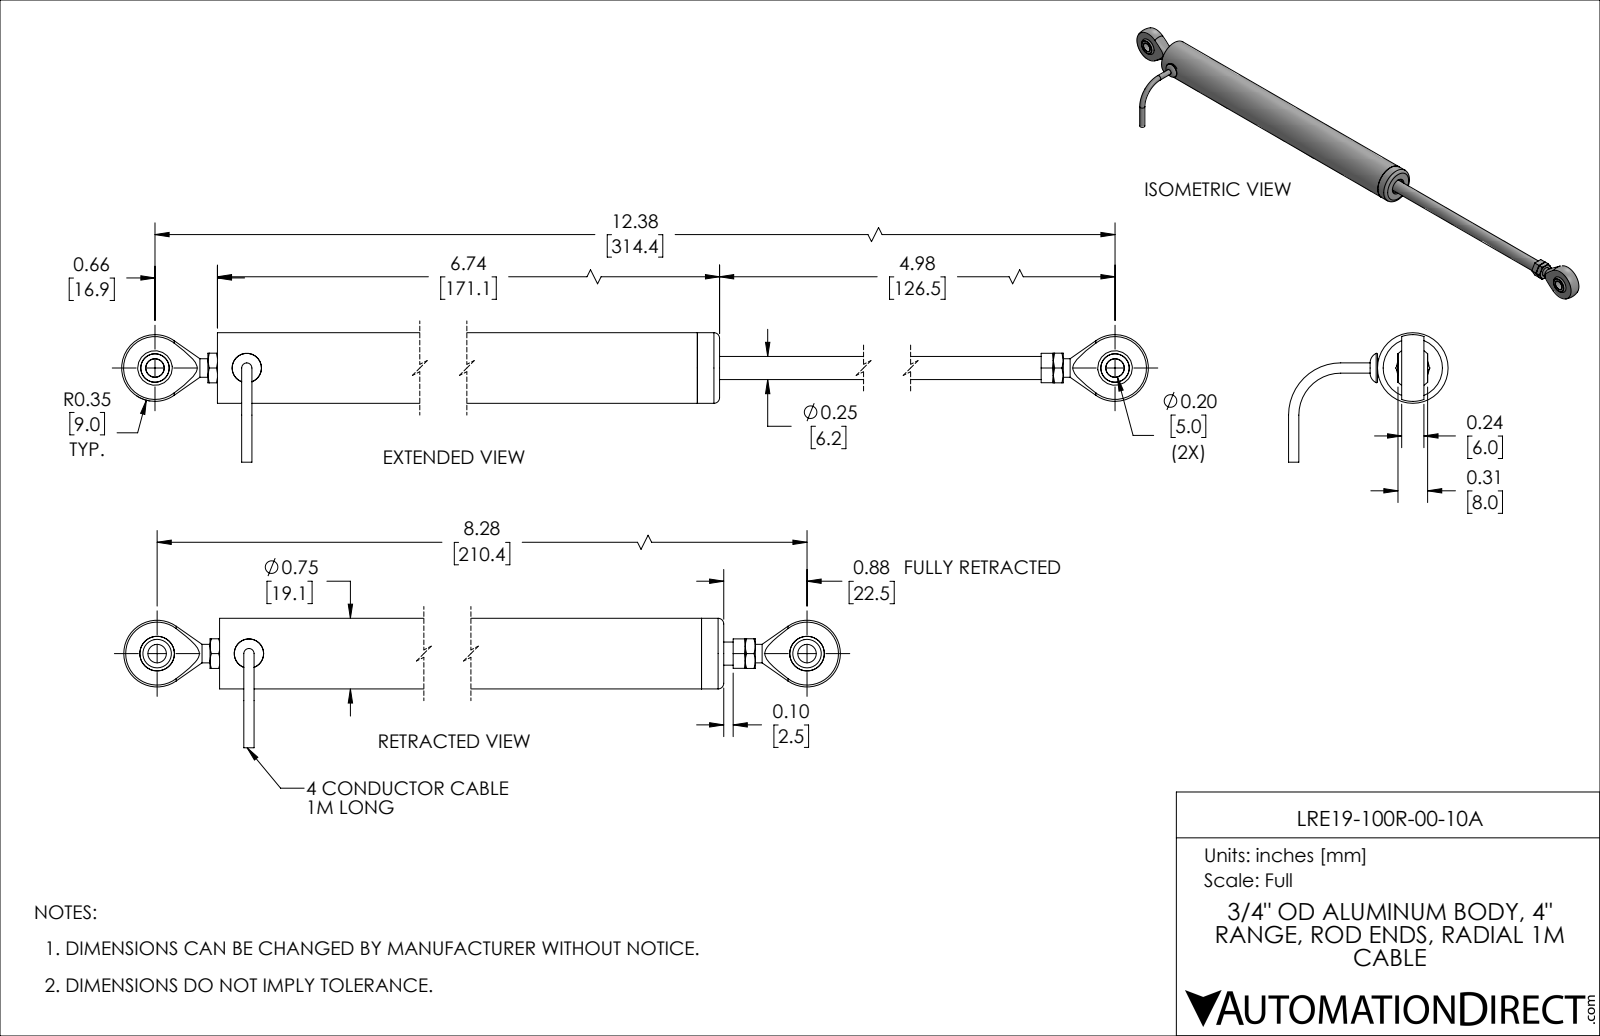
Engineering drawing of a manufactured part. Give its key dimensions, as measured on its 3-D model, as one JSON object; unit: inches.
{"part_name": "LRE19-100R-00-10A", "step_written_by": "SolidWorks 2019 (AUTOMOTIVE_DESIGN)", "units": "inches", "bodies": {"solids": 13, "faces": 163, "planar": 58, "cylindrical": 34, "other": 71}, "overall_size": [8.952, 1.695, 1.375], "volume_in3": 1.364, "surface_area_in2": 48.18, "round_holes": [[0.197, 3], [0.109, 1], [0.165, 1], [0.188, 1], [0.193, 1], [0.221, 1], [0.307, 1], [0.62, 1], [0.625, 1], [0.65, 1], [0.71, 1], [0.725, 1]], "round_bosses_or_shafts": [[0.75, 1], [0.7, 1], [0.624, 1], [0.246, 1], [0.223, 1], [0.218, 1], [0.109, 1]], "face_to_face_distances": [0.236, 0.105, 6.626, 6.731, 6.495, 6.39, 0.236, 0.315, 0.039, 0.276], "hole_center_spacings": [0.975, 7.309, 8.284]}
